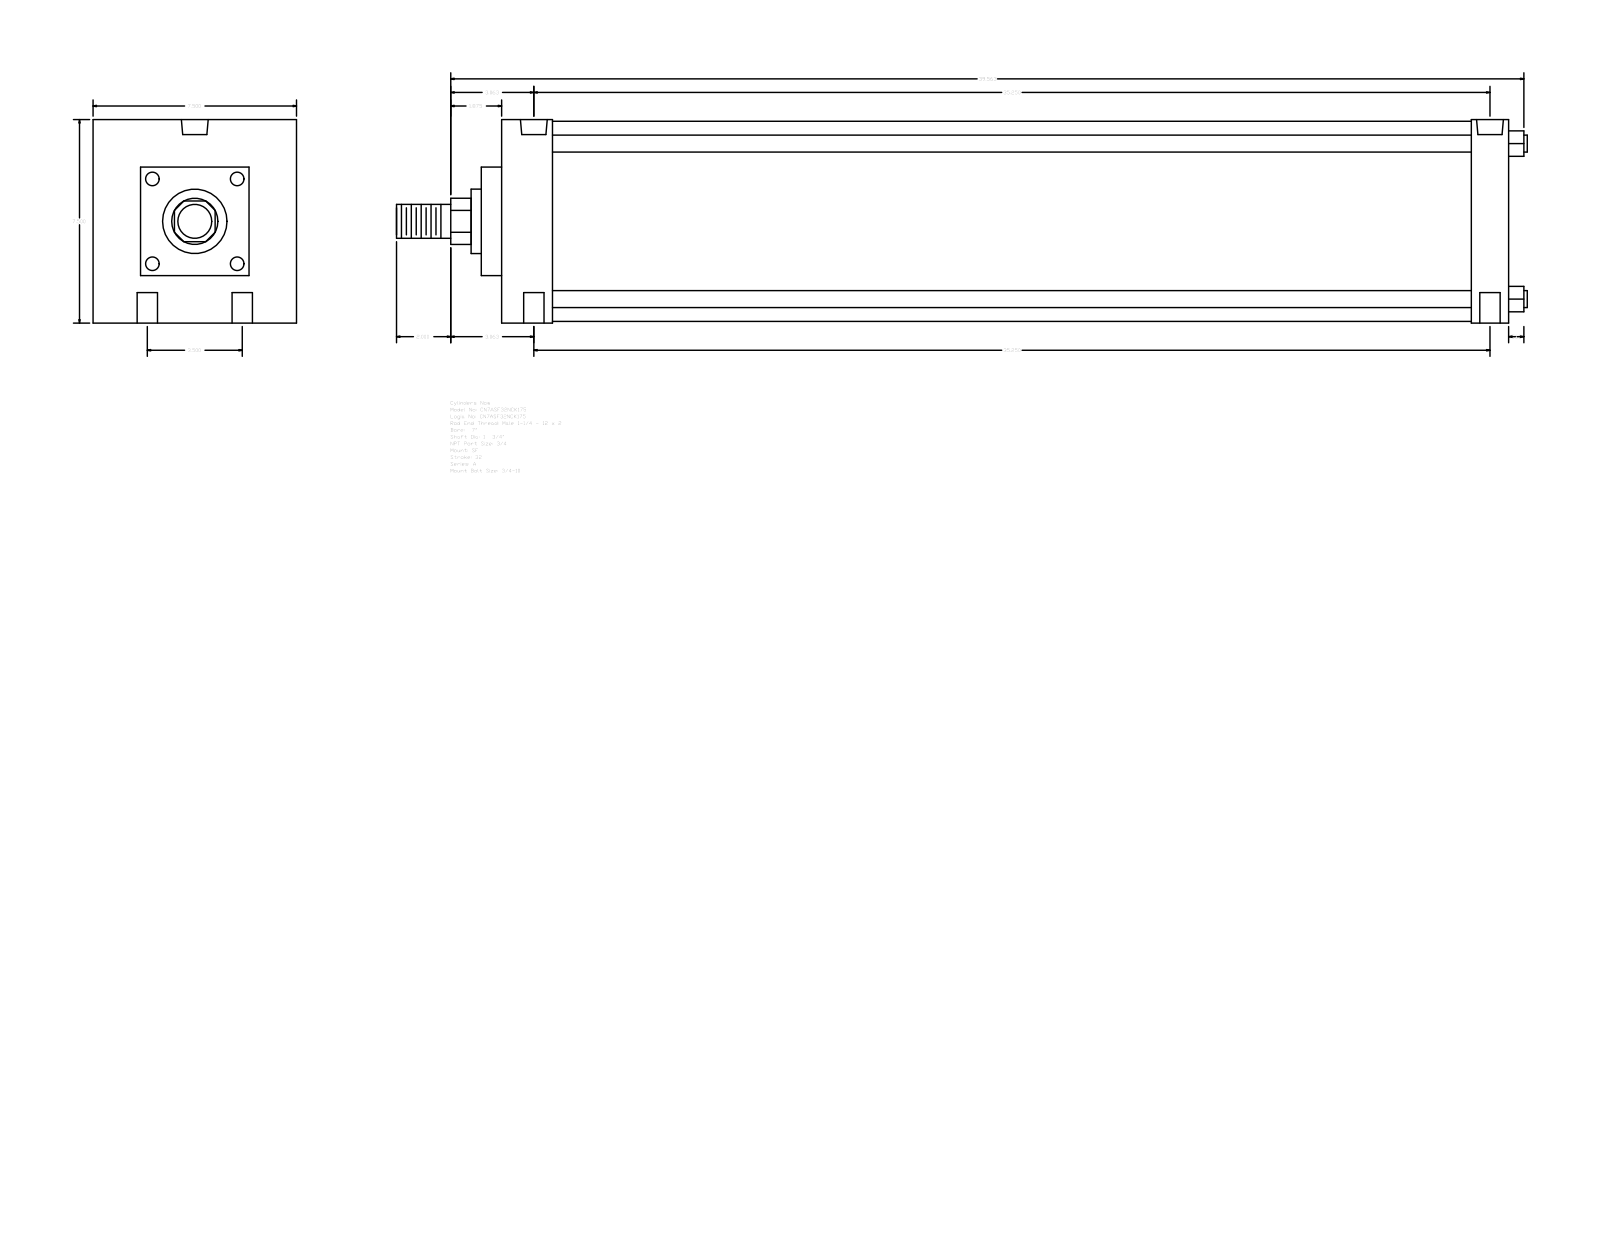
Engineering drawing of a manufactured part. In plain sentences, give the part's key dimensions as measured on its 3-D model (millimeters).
The part is named "A_SF__0700_1.75". Its 3-D file was written by "GSSL Pune (CONFIG_CONTROL_DESIGN)". It is 0 solids with 93 faces: 67 planar, 26 cylindrical and 0 other. Overall it measures 1058.86 by 190.5 by 190.5 millimeters. Round holes: 4 of diameter 19.05, 2 of diameter 15.08, 2 of diameter 25.12. Round bosses or shafts: 4 of diameter 15.88, 1 of diameter 187.32, 1 of diameter 60.33, 1 of diameter 44.45, 1 of diameter 31.75. Partial cylindrical surfaces (rounded edges, fillets, slot ends): 1 of radius 21.63. The main face-to-face distances are 190.5, 942.98, 146.05, 19.05, 47.63, 908.05, 860.42, 895.35, 34.93, 44.45. The hole center spacings are 44.45, 896.45, 895.35, 88.9, 899.75, 884.23.
